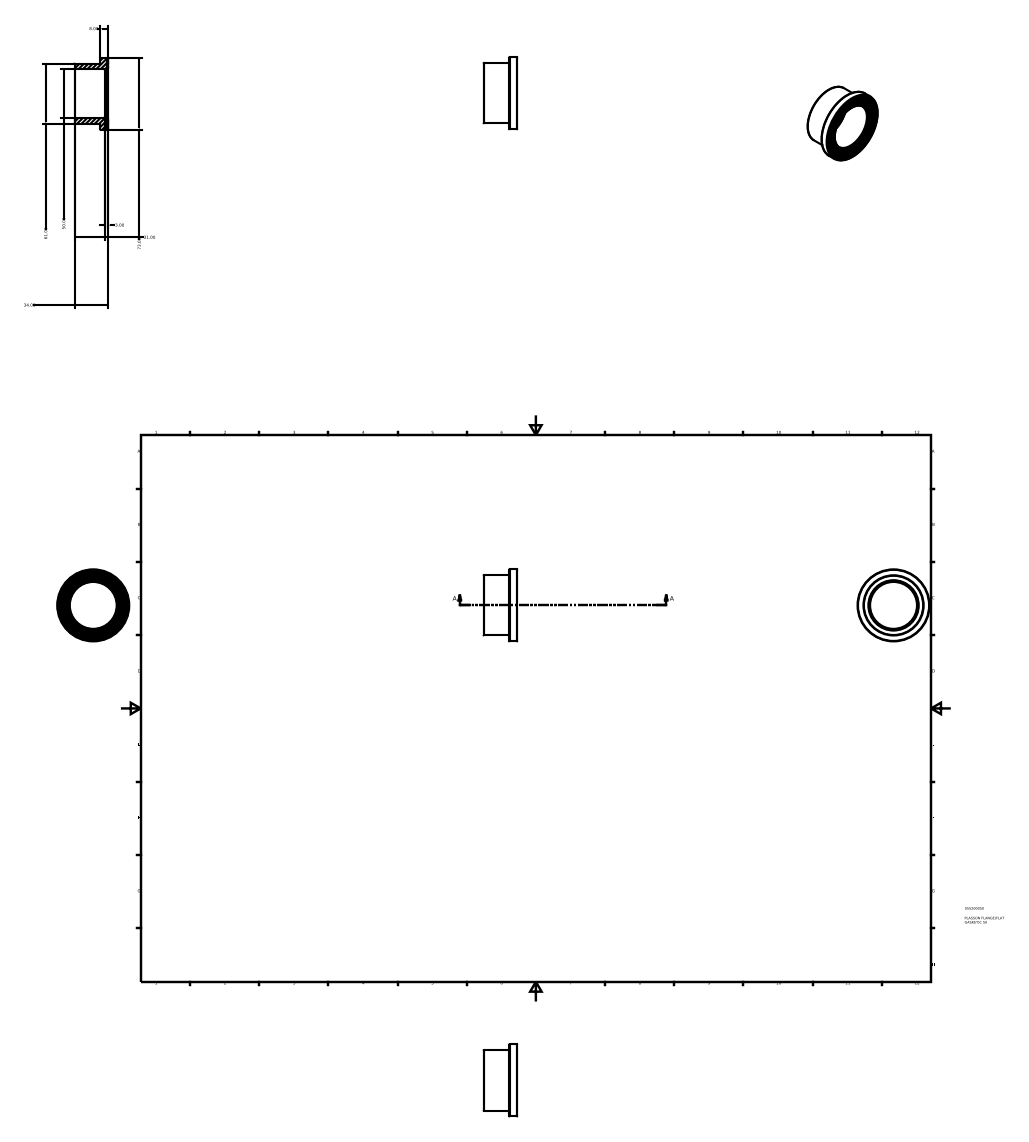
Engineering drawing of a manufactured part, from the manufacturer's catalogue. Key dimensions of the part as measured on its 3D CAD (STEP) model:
Part name (STEP PRODUCT): 055200050
STEP written by: Autodesk Inventor 2015 (AUTOMOTIVE_DESIGN)
Units: millimetres
Bodies: 1 solid, 33 faces (9 planar, 9 cylindrical, 15 other)
Overall size (bounding box): 73 × 73 × 34
Volume: 41 834 mm³ · Surface area: 17 306 mm²
Round holes (diameter × count): ⌀47.5 ×1, ⌀50 ×1, ⌀51.75 ×1, ⌀60.25 ×1, ⌀68.75 ×1
Round bosses / shafts (diameter × count): ⌀73 ×1, ⌀64.5 ×1, ⌀61 ×1, ⌀56 ×1
Main face-to-face distances: 26, 34, 8, 32.8, 6.8, 1.2, 31, 5, 1.8, 3
